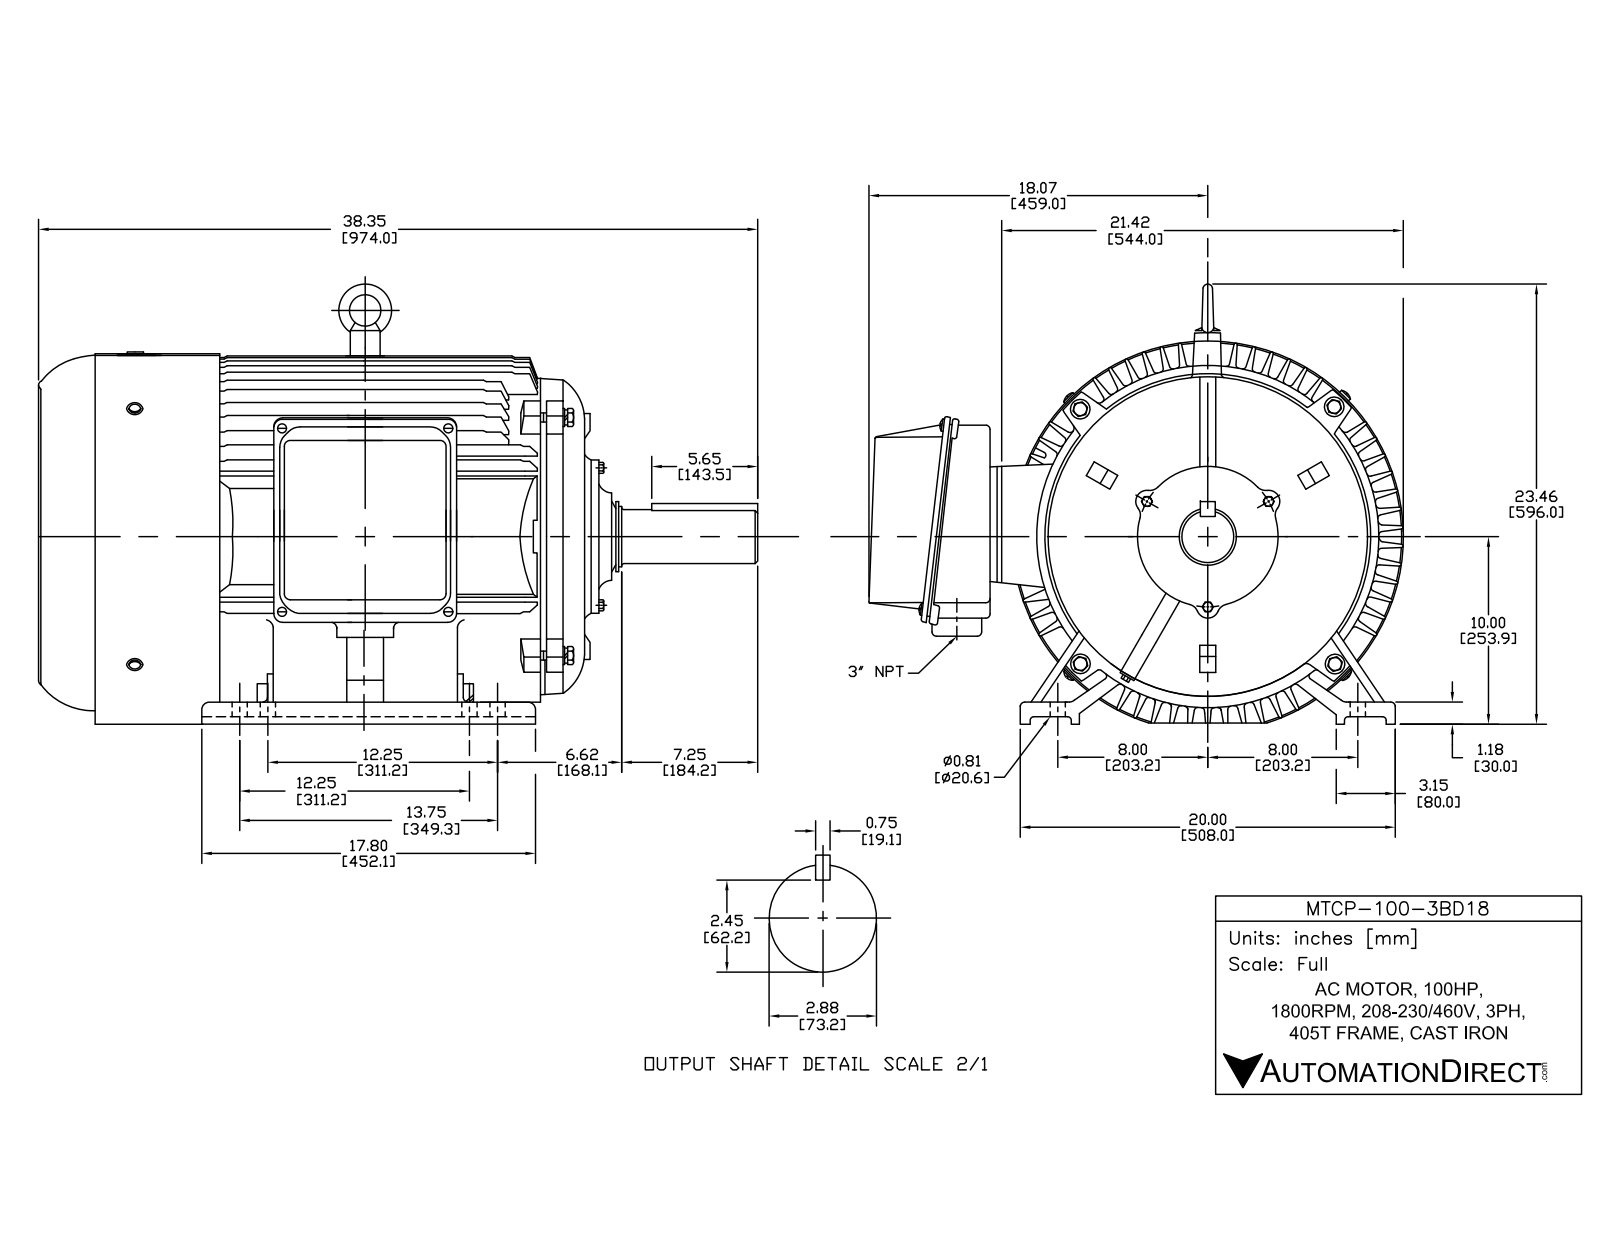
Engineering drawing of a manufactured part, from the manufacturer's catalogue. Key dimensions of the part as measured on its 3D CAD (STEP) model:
Part name (STEP PRODUCT): 30橡皮塞; hex head bolts-full thread grade c gb_GB_FASTENER_BOLT_HHBFTC M8X16-N; plain washers-chamfered--normal series-a gb_GB_FASTENER_WASHER_SWCA 8; MTCP405T (+8 more)
STEP written by: SolidWorks 2017 (AUTOMOTIVE_DESIGN)
Units: millimetres
Bodies: 68 solids, 4257 faces (1008 planar, 1632 cylindrical, 1617 other)
Overall size (bounding box): 977.1 × 740.07 × 602.4
Volume: 25 640 000 mm³ · Surface area: 5 965 000 mm²
Round holes (diameter × count): ⌀10 ×14, ⌀12 ×10, ⌀6.8 ×8, ⌀21 ×8, ⌀2.5 ×4, ⌀7 ×4, ⌀8.4 ×4, ⌀8.5 ×4, ⌀8.68 ×4, ⌀9 ×4, ⌀10.2 ×4, ⌀12.9 ×4
Round bosses / shafts (diameter × count): ⌀8 ×12, ⌀10 ×7, ⌀24 ×4, ⌀19.1 ×4, ⌀16 ×4, ⌀12.88 ×4, ⌀12 ×4, ⌀547 ×1
Partial cylindrical surfaces — rounded edges, fillets, slot ends (radius × count): R1 ×256, R0.5 ×106, R3 ×84, R5 ×65, R1.5 ×41, R9 ×26, R6 ×24, R4.5 ×18
Main face-to-face distances: 6, 2, 605, 9, 141.6, 139.6, 10, 4, 24, 746.6
Hole centre spacings: 130, 87.5, 97.5, 228, 10, 92.91, 160.29, 177.97
